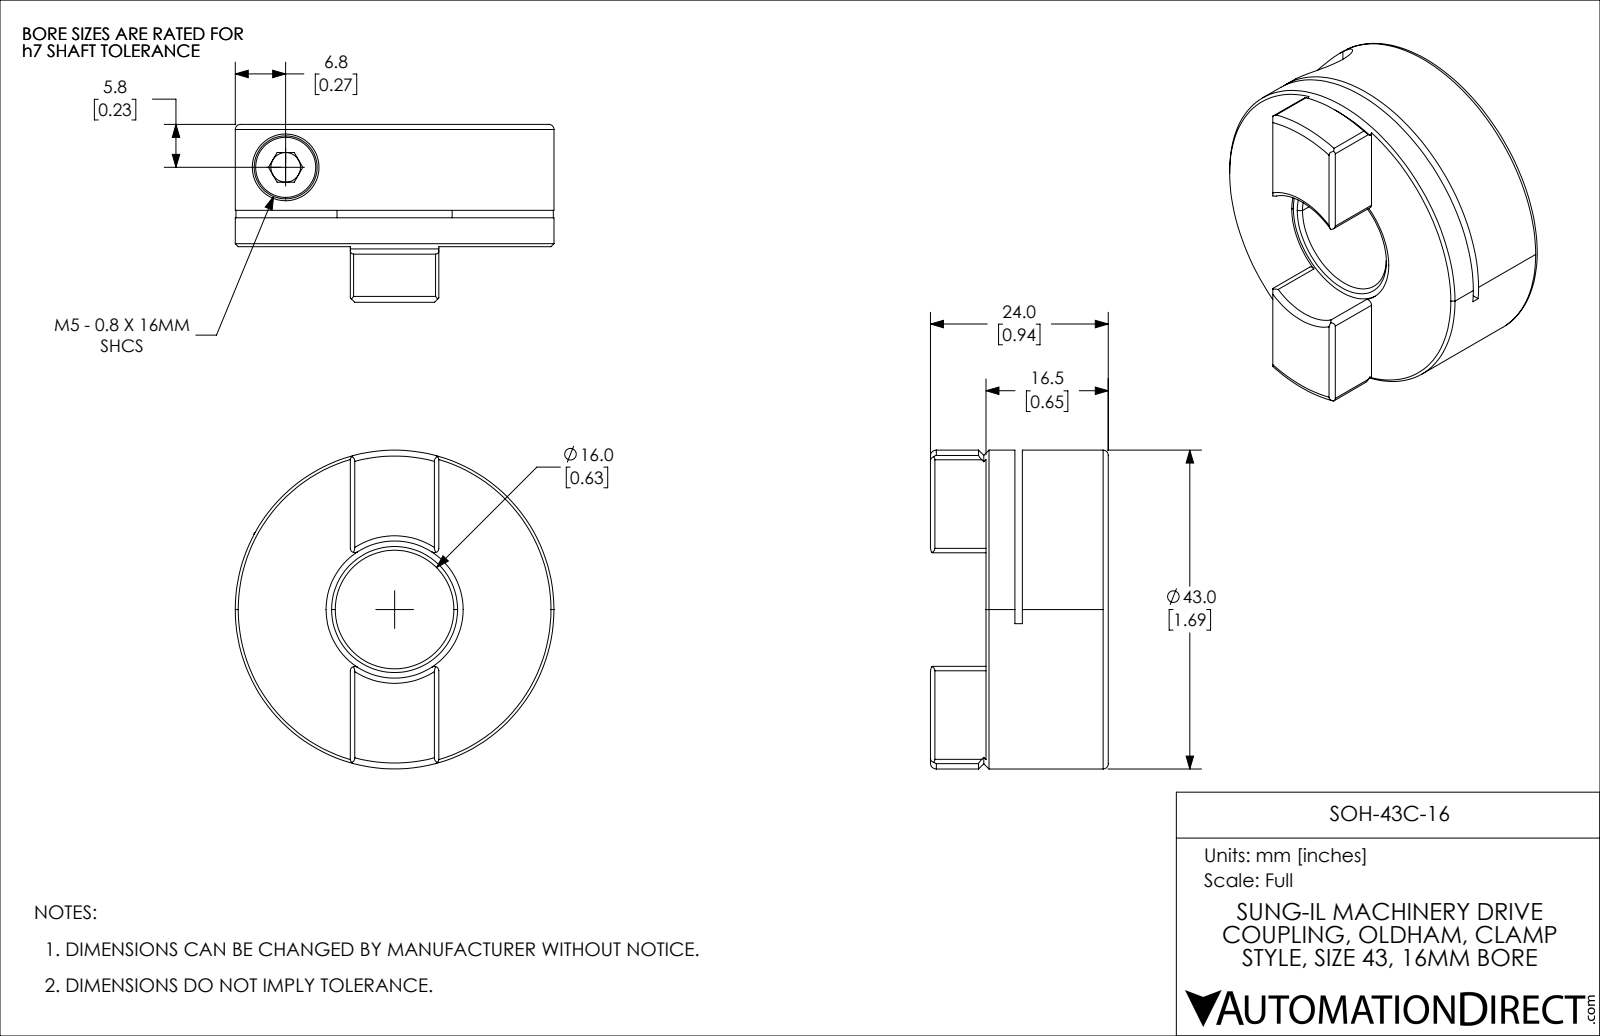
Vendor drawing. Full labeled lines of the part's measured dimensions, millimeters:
Part name (STEP PRODUCT): SOH-43C-16
STEP written by: SolidWorks 2021 (CONFIG_CONTROL_DESIGN)
Units: millimetres
Bodies: 2 solids, 95 faces (39 planar, 33 cylindrical, 23 other)
Overall size (bounding box): 43 × 43 × 24
Volume: 21 481 mm³ · Surface area: 8 810 mm²
Round holes (diameter × count): ⌀4 ×1, ⌀4.2 ×1, ⌀5.4 ×1, ⌀9 ×1, ⌀16 ×1, ⌀18.5 ×1
Round bosses / shafts (diameter × count): ⌀43 ×1, ⌀8.5 ×1, ⌀5 ×1
Partial cylindrical surfaces — rounded edges, fillets, slot ends (radius × count): R0.6 ×8, R37.5 ×1
Main face-to-face distances: 16.5, 12.6, 3.9, 11.6, 1, 4.9, 12.4, 24, 11.4, 7.5
